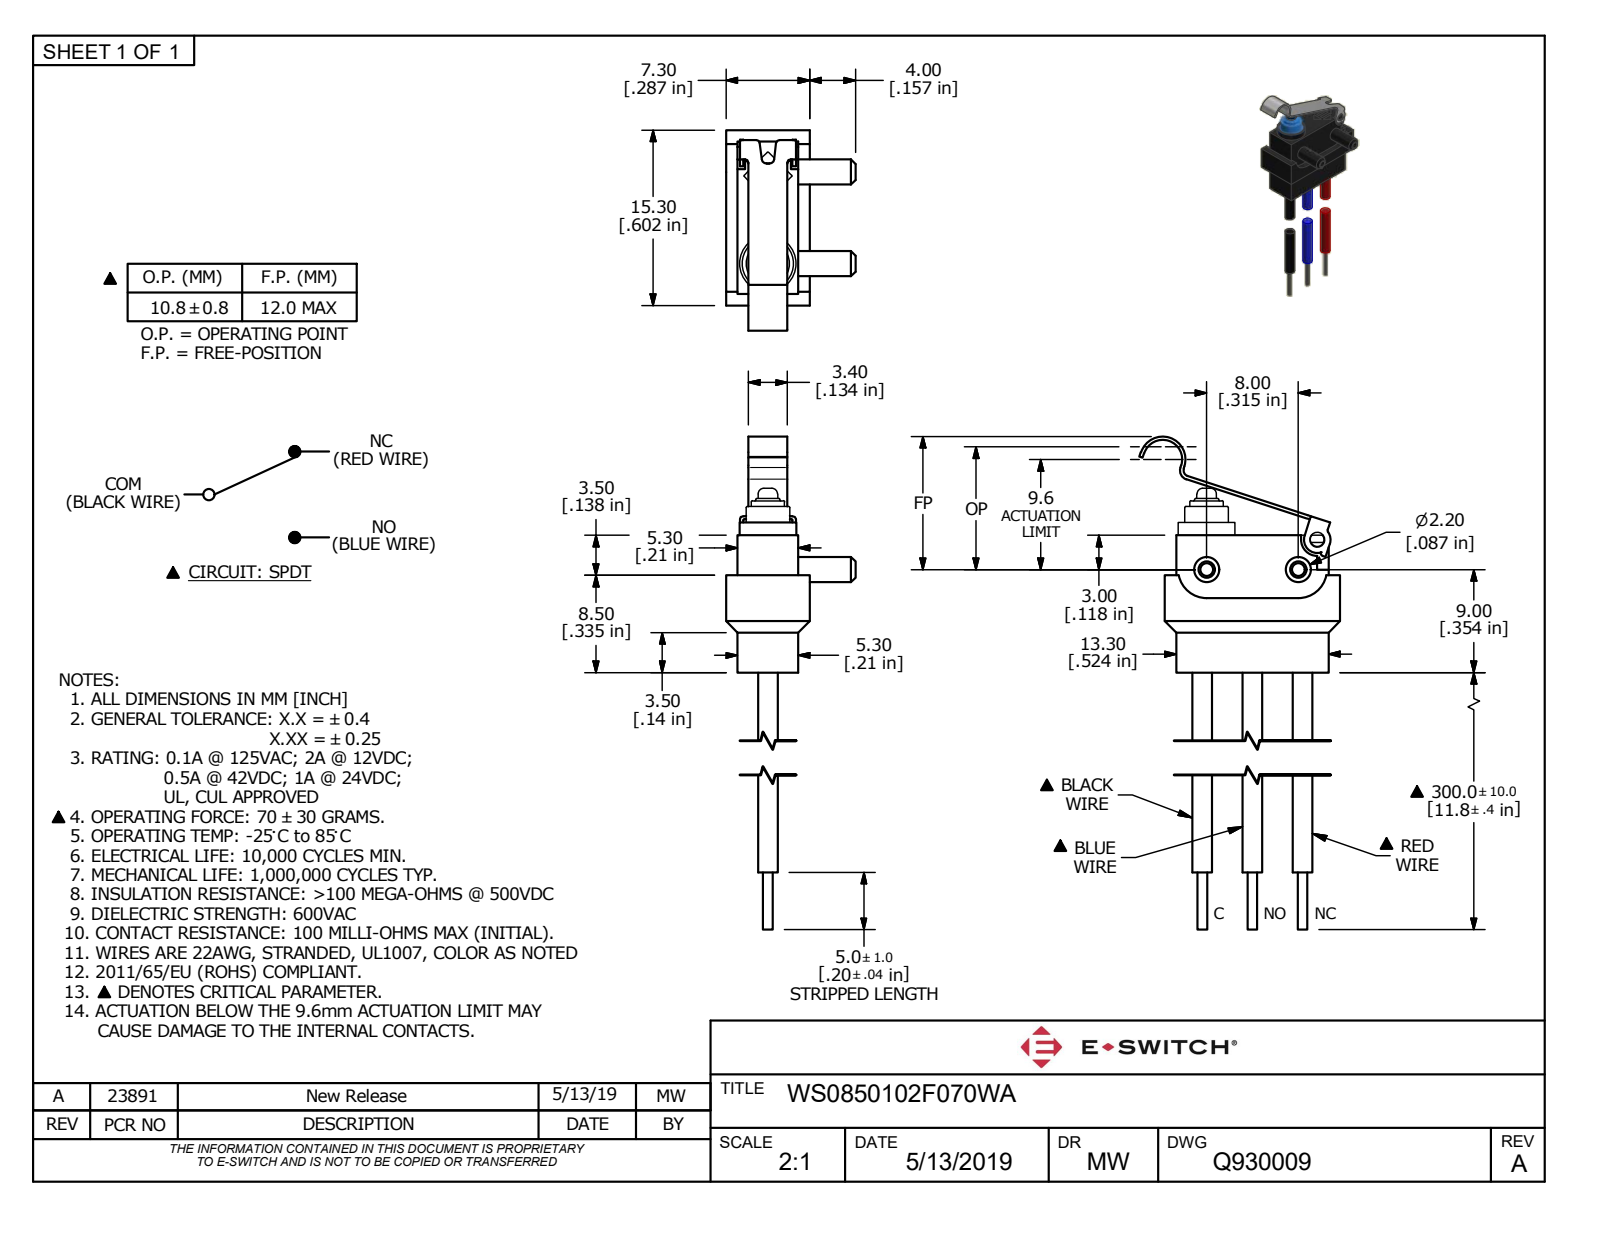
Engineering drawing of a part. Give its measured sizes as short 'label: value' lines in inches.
name: WS0850102F070WA
written by: Autodesk Inventor 2012 (CONFIG_CONTROL_DESIGN)
unit: in
bodies: 2 solids, 292 faces (168 planar, 94 cylindrical, 30 other)
size: 12.619 × 0.692 × 0.445
volume: 0.178 in³; area: 9.536 in²
holes: 2× ⌀0.043, 1× ⌀0.051, 1× ⌀0.177
bosses: 6× ⌀0.031, 4× ⌀0.067, 3× ⌀0.033, 2× ⌀0.087, 1× ⌀0.195, 1× ⌀0.15, 1× ⌀0.114
rounds: 7× R0.024, 6× R0.012, 6× R0.037, 3× R0.016, 2× R0.004, 2× R0.01, 2× R0.018, 2× R0.098
face distances: 0.031, 0.039, 0.217, 0.177, 0.071, 0.209, 0.248, 0.146, 0.256, 0.563
hole spacings: 0.121, 0.315, 0.393
